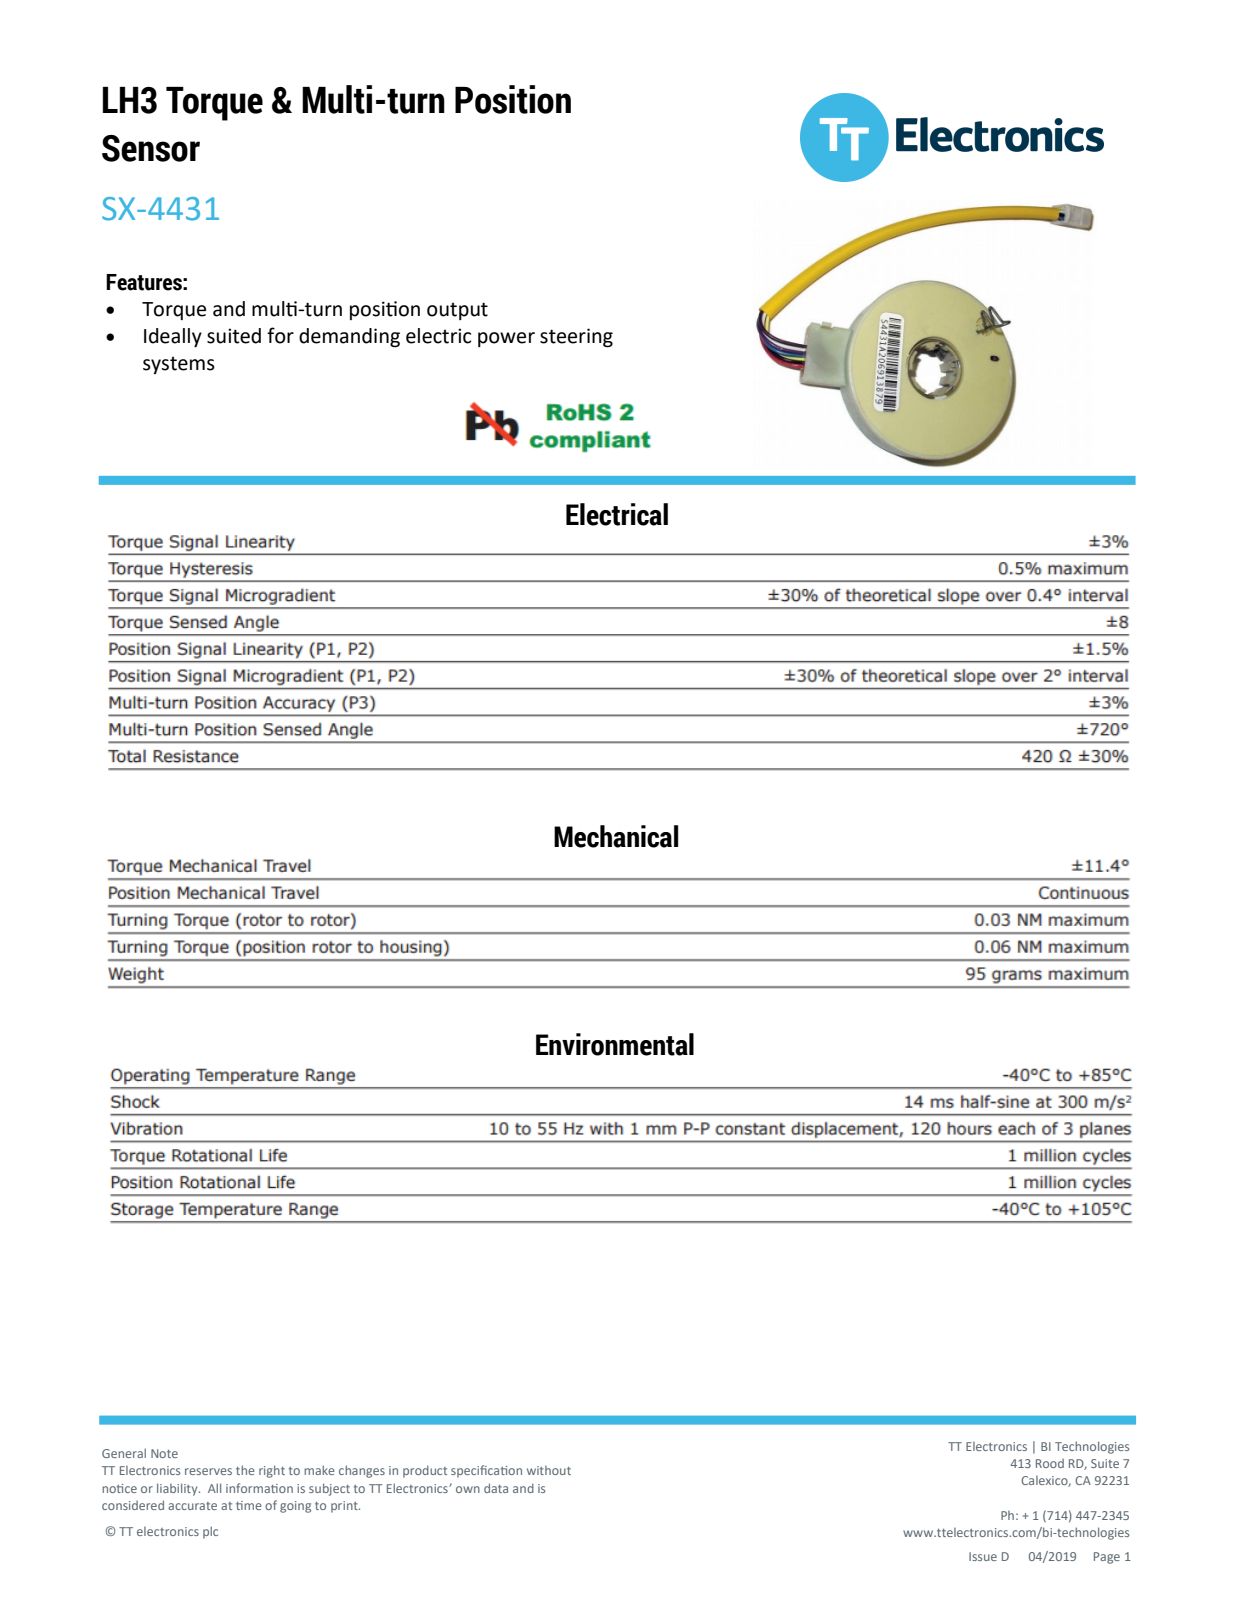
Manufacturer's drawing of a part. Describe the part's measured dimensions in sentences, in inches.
The part is named "SX-4431A_SW0001". Its 3-D file was written by "PRO/ENGINEER BY PARAMETRIC TECHNOLOGY CORPORATION, 2011490 (CONFIG_CONTROL_DESIGN)". It is 15 solids with 1879 faces: 859 planar, 673 cylindrical and 347 other. Overall it measures 8.597 by 3.2 by 1.728 inches. Its volume is 5.395 cubic inches and its surface area 50 square inches. Round holes: 7 of diameter 0.042, 5 of diameter 0.039, 1 of diameter 0.049, 1 of diameter 0.29, 1 of diameter 0.985, 1 of diameter 1.046, 1 of diameter 1.126, 1 of diameter 1.146, 1 of diameter 1.2, 1 of diameter 1.255, 1 of diameter 3.15. Round bosses or shafts: 27 of diameter 0.04, 6 of diameter 0.047, 1 of diameter 3.2, 1 of diameter 3.142, 1 of diameter 3.1, 1 of diameter 3.056, 1 of diameter 1.345, 1 of diameter 1.234. Partial cylindrical surfaces (rounded edges, fillets, slot ends): 72 of radius 0.007, 72 of radius 0.012, 63 of radius 0.01, 44 of radius 0.005, 32 of radius 0.01, 21 of radius 0.02, 19 of radius 0.016, 18 of radius 0.006. The main face-to-face distances are 0.719, 0.087, 0.521, 0.108, 0.012, 0.065, 0.729, 0.531, 0.11, 0.173. The hole center spacings are 0.115, 0.23, 0.23, 0.345, 0.345, 0.46, 0.575, 0.115.
